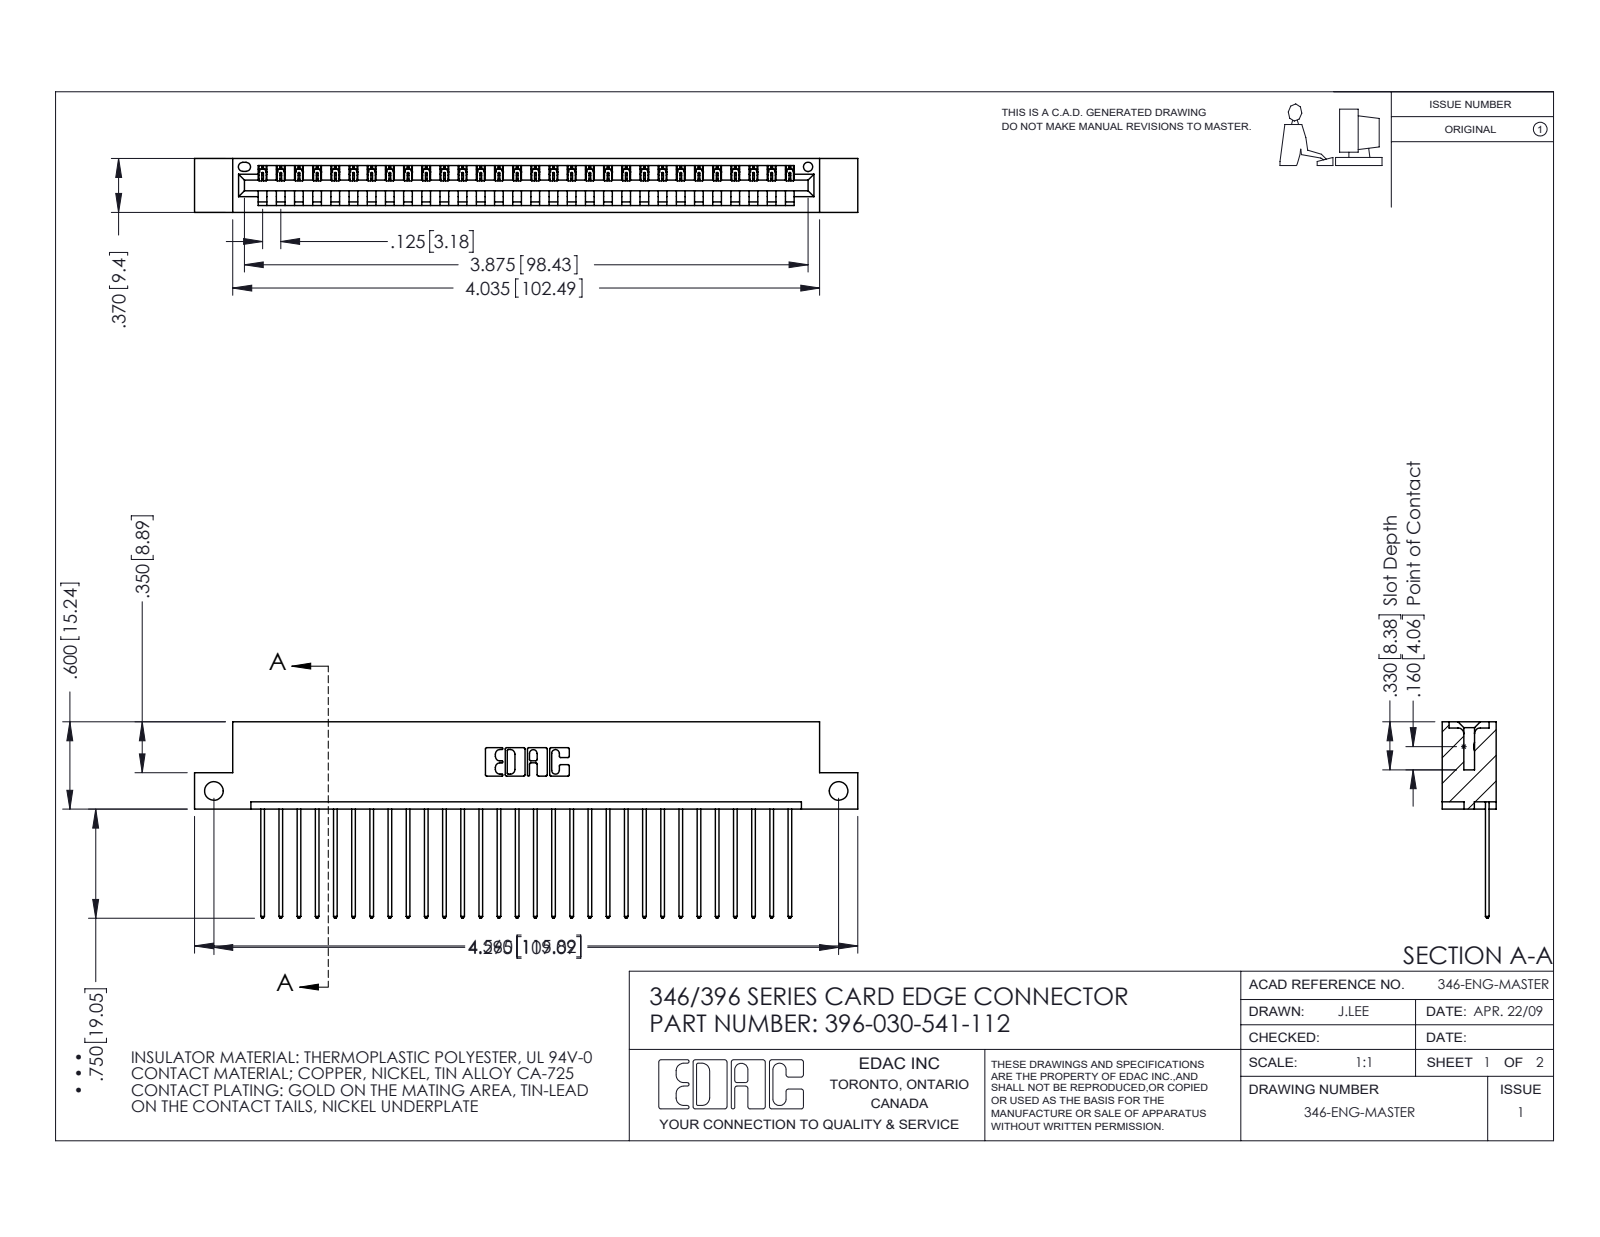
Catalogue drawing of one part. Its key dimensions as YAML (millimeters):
part_name: "396-030-541-112; 345-292-001_345-293-141; 346 Part_Flush Mounting Lugs - Side Mount"
step_written_by: "SolidWorks 2016 (CONFIG_CONTROL_DESIGN)"
units: millimeters
bodies: {solids: 31, faces: 1862, planar: 1276, cylindrical: 586, other: 0}
overall_size: [115.8, 34.3, 9.4]
volume: 11000
surface_area: 14080
round_holes:
  - {diameter: 3.3, count: 2}
  - {diameter: 1.6, count: 1}
partial_cylinders:
  - {radius: 0.2, count: 60}
  - {radius: 0.3, count: 60}
  - {radius: 0.3, count: 22}
  - {radius: 0.2, count: 6}
  - {radius: 0.8, count: 6}
  - {radius: 0.7, count: 3}
  - {radius: 0.8, count: 2}
  - {radius: 1, count: 2}
face_to_face_distances: [1.2, 8.2, 6.4, 9.4, 1.8, 7.6, 0.6, 3.8, 5.6, 2.5]
hole_center_spacings: [109.1]
